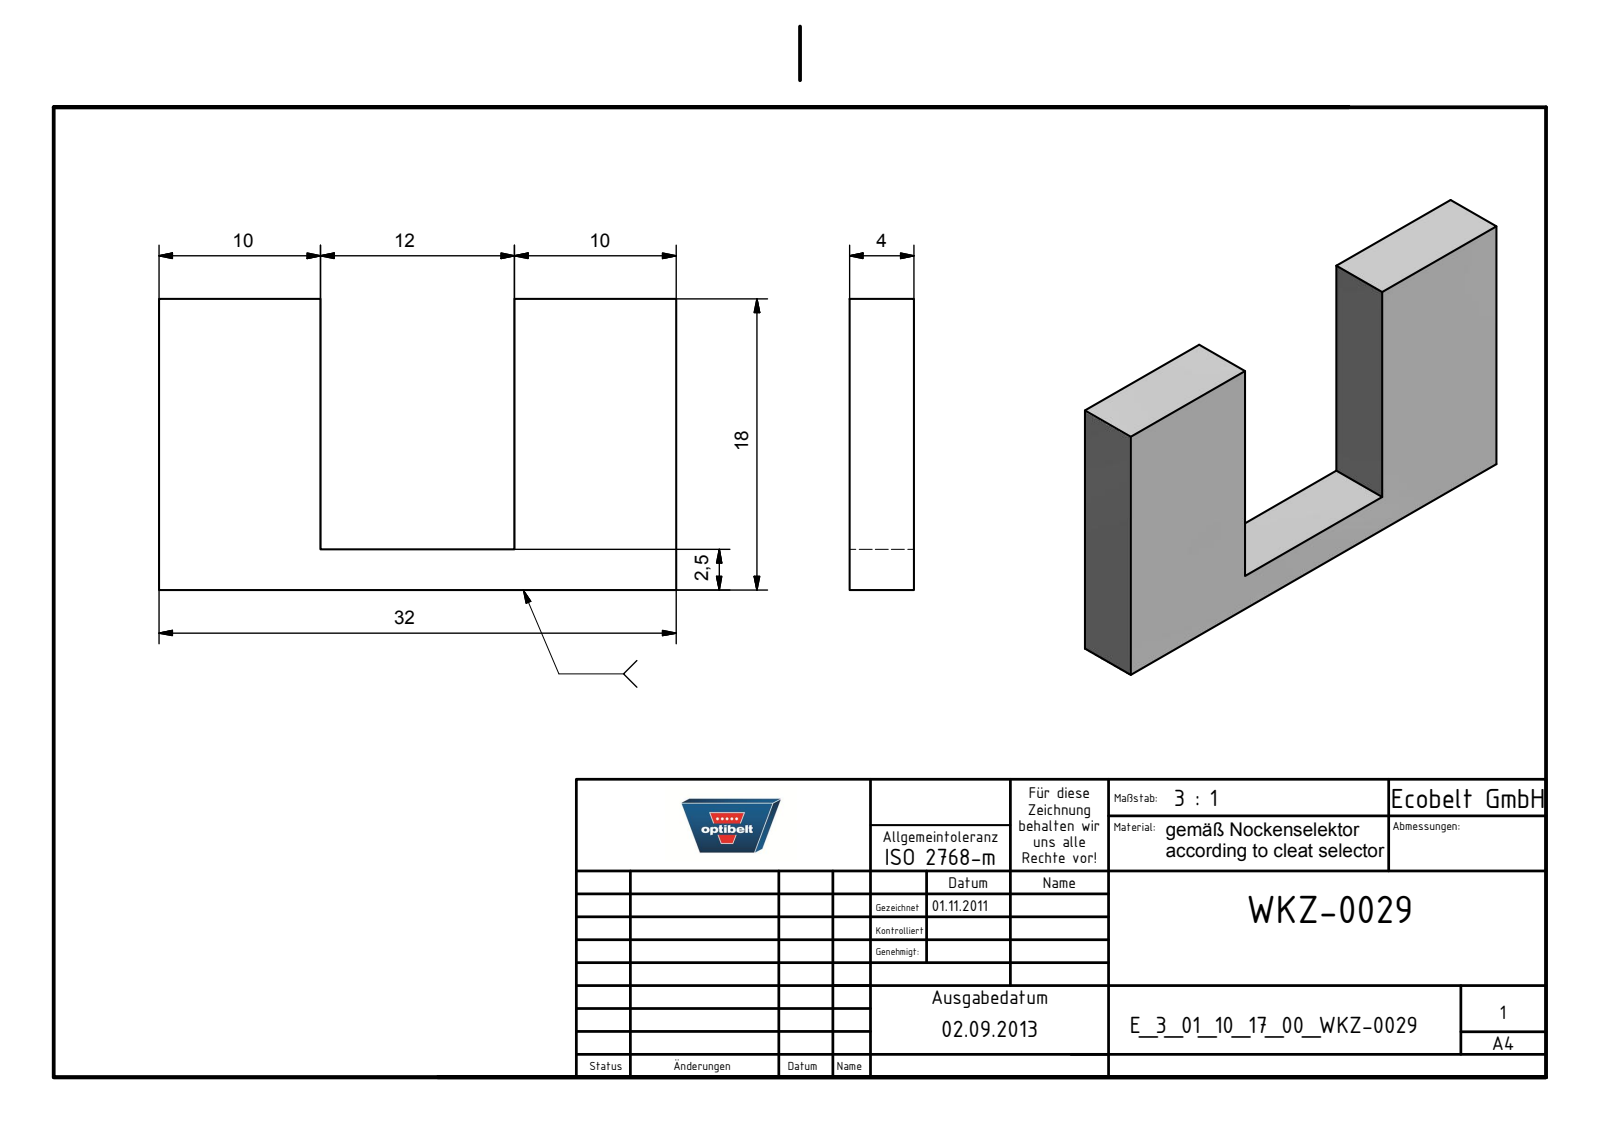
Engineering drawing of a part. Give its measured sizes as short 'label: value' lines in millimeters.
name: E_3_01_10_17_00_WKZ-0029
written by: Autodesk Inventor 2021 (AUTOMOTIVE_DESIGN)
unit: mm
bodies: 1 solid, 10 faces (10 planar, 0 cylindrical, 0 other)
size: 32 × 18 × 4
volume: 1 560 mm³; area: 1 304 mm²
face distances: 4, 10, 22, 18, 32, 12, 2.5, 15.5
